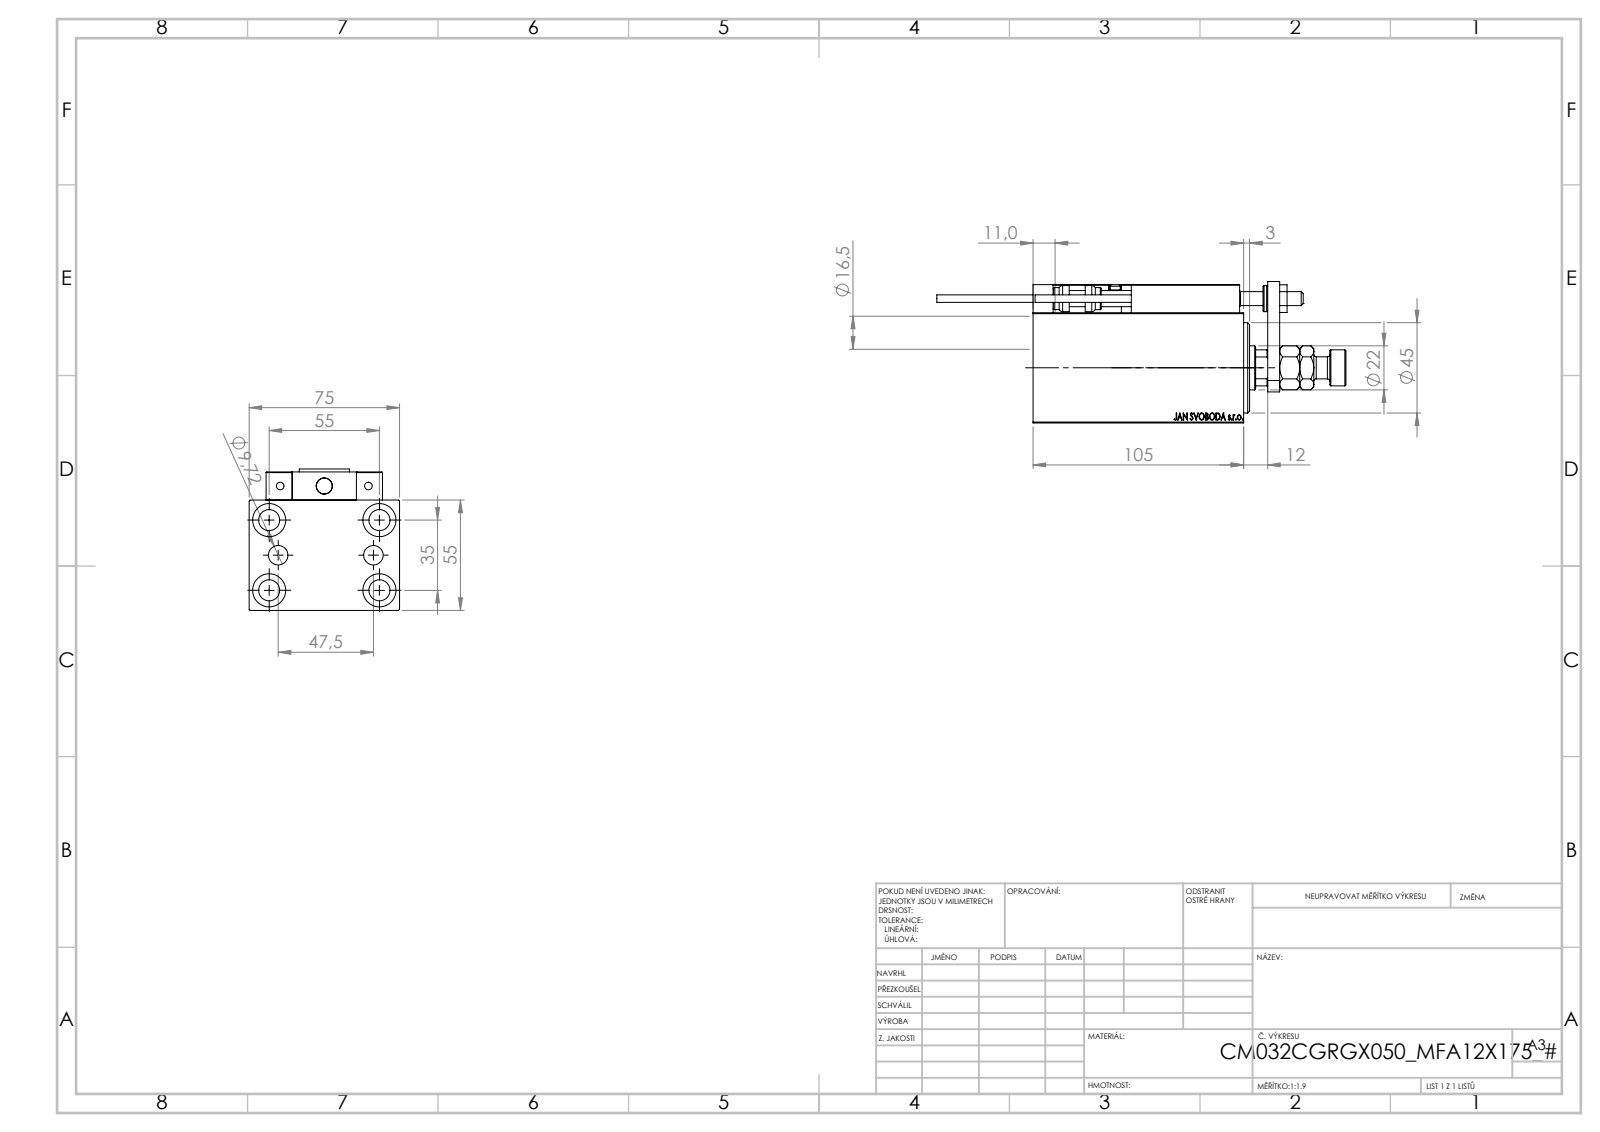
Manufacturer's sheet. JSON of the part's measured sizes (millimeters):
{"part_name": "V450CM_VC_B; V450CM_C_VCP; NUT_D12; X_Y_MFA (+7 more)", "step_written_by": "SolidWorks 2019 (CONFIG_CONTROL_DESIGN)", "units": "millimeters", "bodies": {"solids": 24, "faces": 1330, "planar": 576, "cylindrical": 188, "other": 566}, "overall_size": [204, 75, 70.5], "volume_mm3": 423445, "surface_area_mm2": 108285, "round_holes": [[4, 6], [8, 5], [10.5, 5], [16.5, 5], [3.2, 4], [5, 2], [9.72, 2], [7, 1], [22, 1], [25.5, 1], [32, 1], [34, 1]], "round_bosses_or_shafts": [[11, 2], [5, 2], [3.8, 2], [18, 1], [13, 1]], "partial_cylinders_radius": [[0.3, 30], [3, 2], [10.5, 1]], "face_to_face_distances": [55, 75, 14, 10, 69, 3, 5, 23, 18, 25], "hole_center_spacings": [17.9, 32.6, 54.16, 11.37, 20, 23.75, 29.59, 29.69]}
